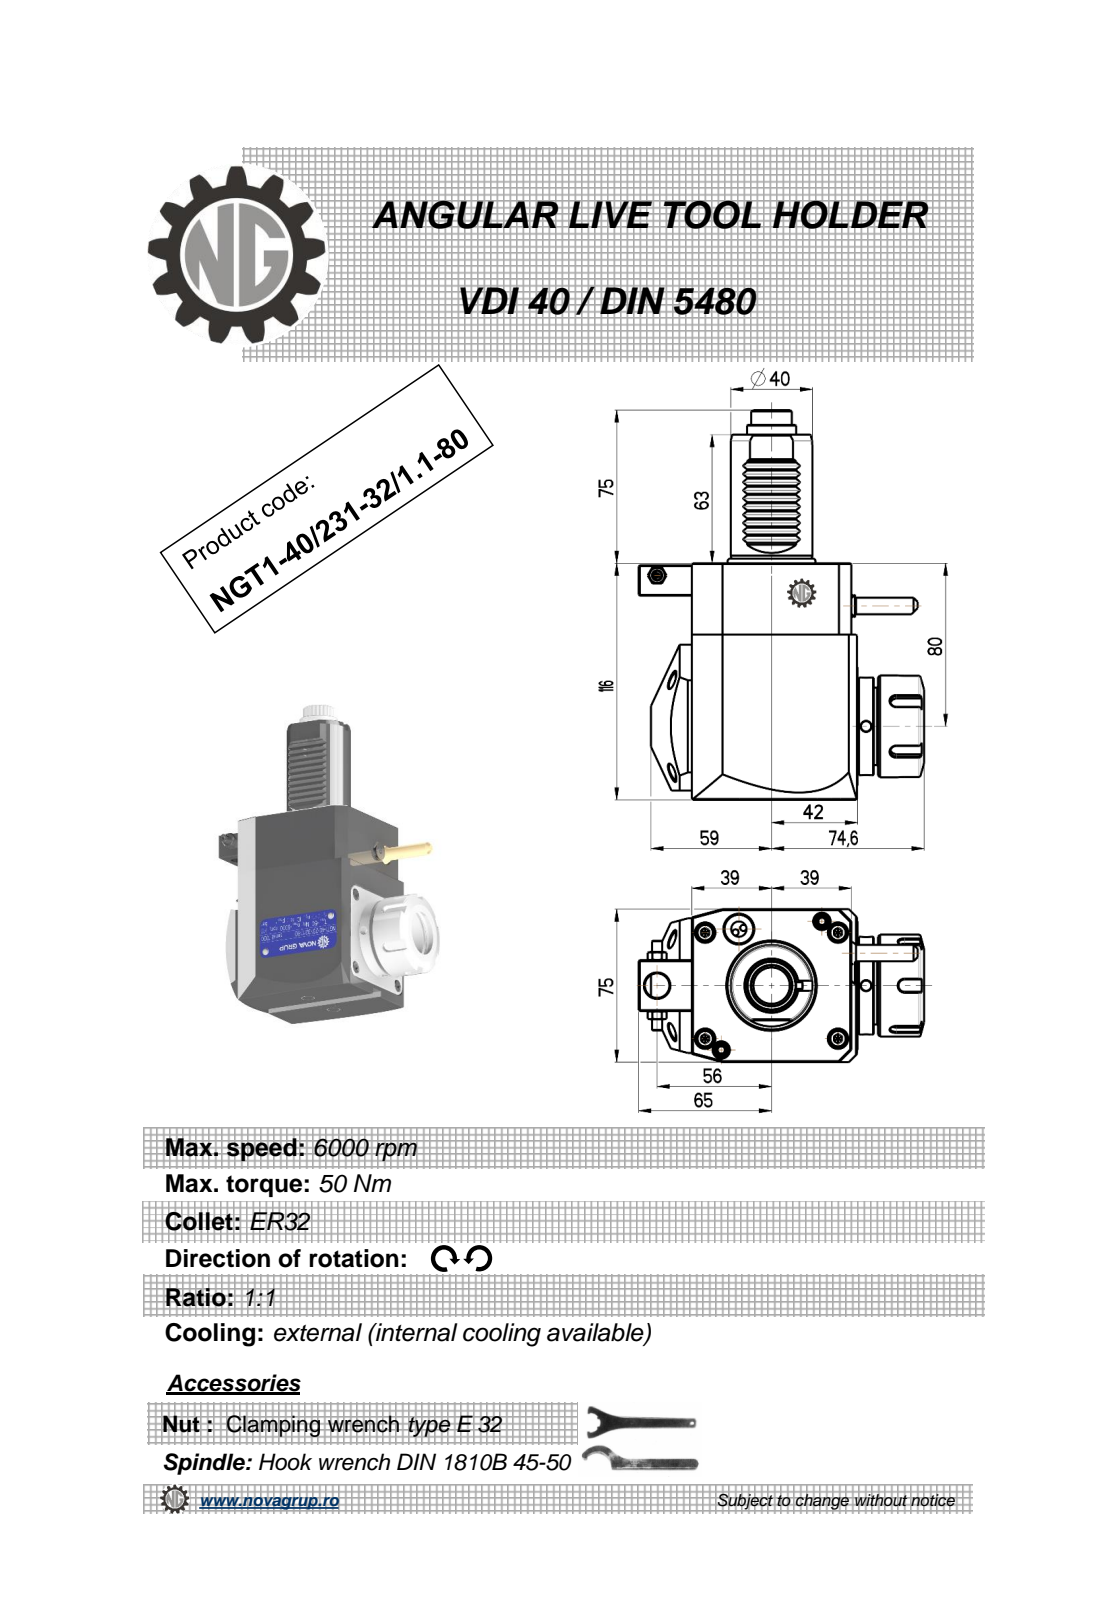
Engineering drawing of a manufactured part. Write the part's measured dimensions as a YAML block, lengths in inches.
part_name: "NGT1_40_231_32_1_1_80"
step_written_by: "PRO/ENGINEER BY PARAMETRIC TECHNOLOGY CORPORATION, 2010280 (CONFIG_CONTROL_DESIGN)"
units: inches
bodies: {solids: 1, faces: 532, planar: 193, cylindrical: 185, other: 154}
overall_size: [7.52, 5.496, 3.016]
volume: 53.79
surface_area: 109.2
round_holes:
  - {diameter: 0.197, count: 3}
  - {diameter: 0.118, count: 1}
  - {diameter: 0.165, count: 1}
  - {diameter: 0.374, count: 1}
  - {diameter: 0.472, count: 1}
  - {diameter: 1.063, count: 1}
round_bosses_or_shafts:
  - {diameter: 1.969, count: 1}
  - {diameter: 1.89, count: 1}
  - {diameter: 1.614, count: 1}
  - {diameter: 1.575, count: 1}
  - {diameter: 0.945, count: 1}
  - {diameter: 0.441, count: 1}
  - {diameter: 0.353, count: 1}
  - {diameter: 0.315, count: 1}
partial_cylinders:
  - {radius: 0.082, count: 48}
  - {radius: 0.01, count: 12}
  - {radius: 0.012, count: 10}
  - {radius: 0.009, count: 6}
  - {radius: 0.118, count: 5}
  - {radius: 0.357, count: 1}
  - {radius: 0.391, count: 1}
  - {radius: 0.591, count: 1}
face_to_face_distances: [2.953, 4.567, 3.189, 0.118, 3.071, 3.181, 0.11, 0.177, 0.295, 0.984]
hole_center_spacings: [0.799, 2.407, 2.815, 4.026, 4.969]
